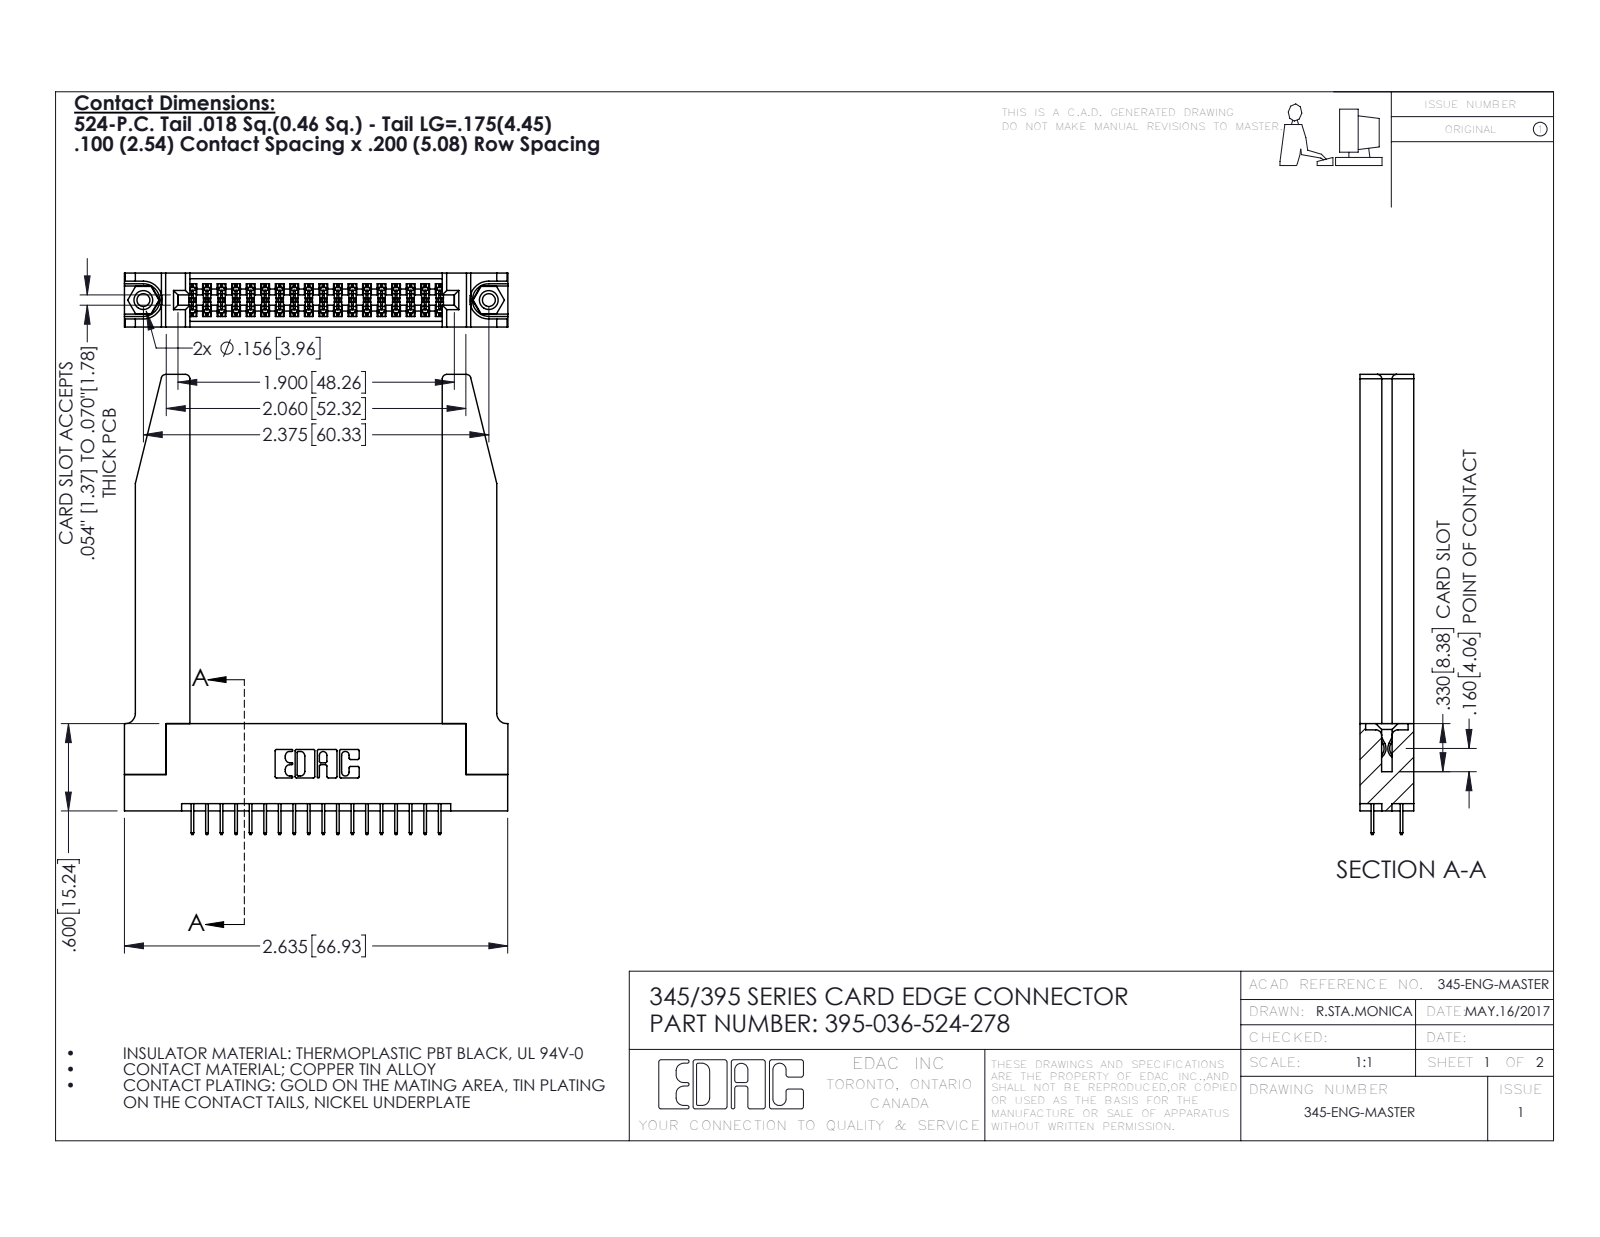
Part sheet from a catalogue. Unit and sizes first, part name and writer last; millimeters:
Units: millimetres
Overall size (bounding box): 80.3 × 67 × 9.4
Round holes (diameter × count): ⌀2.3 ×2, ⌀3.2 ×2, ⌀4 ×2, ⌀1.6 ×1
Round bosses / shafts (diameter × count): ⌀3.9 ×2
Partial cylindrical surfaces — rounded edges, fillets, slot ends (radius × count): R0.2 ×54, R0.3 ×22, R0.8 ×8, R0.2 ×6, R0.8 ×6, R0.7 ×3, R0.4 ×2, R0.5 ×2
Main face-to-face distances: 9.4, 1.8, 7.6, 5.1, 3.8, 3.8, 2.5, 6.9, 0.6, 5.7
Hole centre spacings: 6.9, 54.4, 60.3
Volume: 14 000 mm³ · Surface area: 15 430 mm²
Bodies: 41 solids, 2304 faces (1626 planar, 626 cylindrical, 52 other)
Part name (STEP PRODUCT): 345-292-001_345-293-124; 395-036-524-278; 345 Part_Flush Mounting Lugs - 0.156 Dia-TH; 345-250-001_345-250-001-102 (+1 more)
STEP written by: SolidWorks 2016 (CONFIG_CONTROL_DESIGN)
